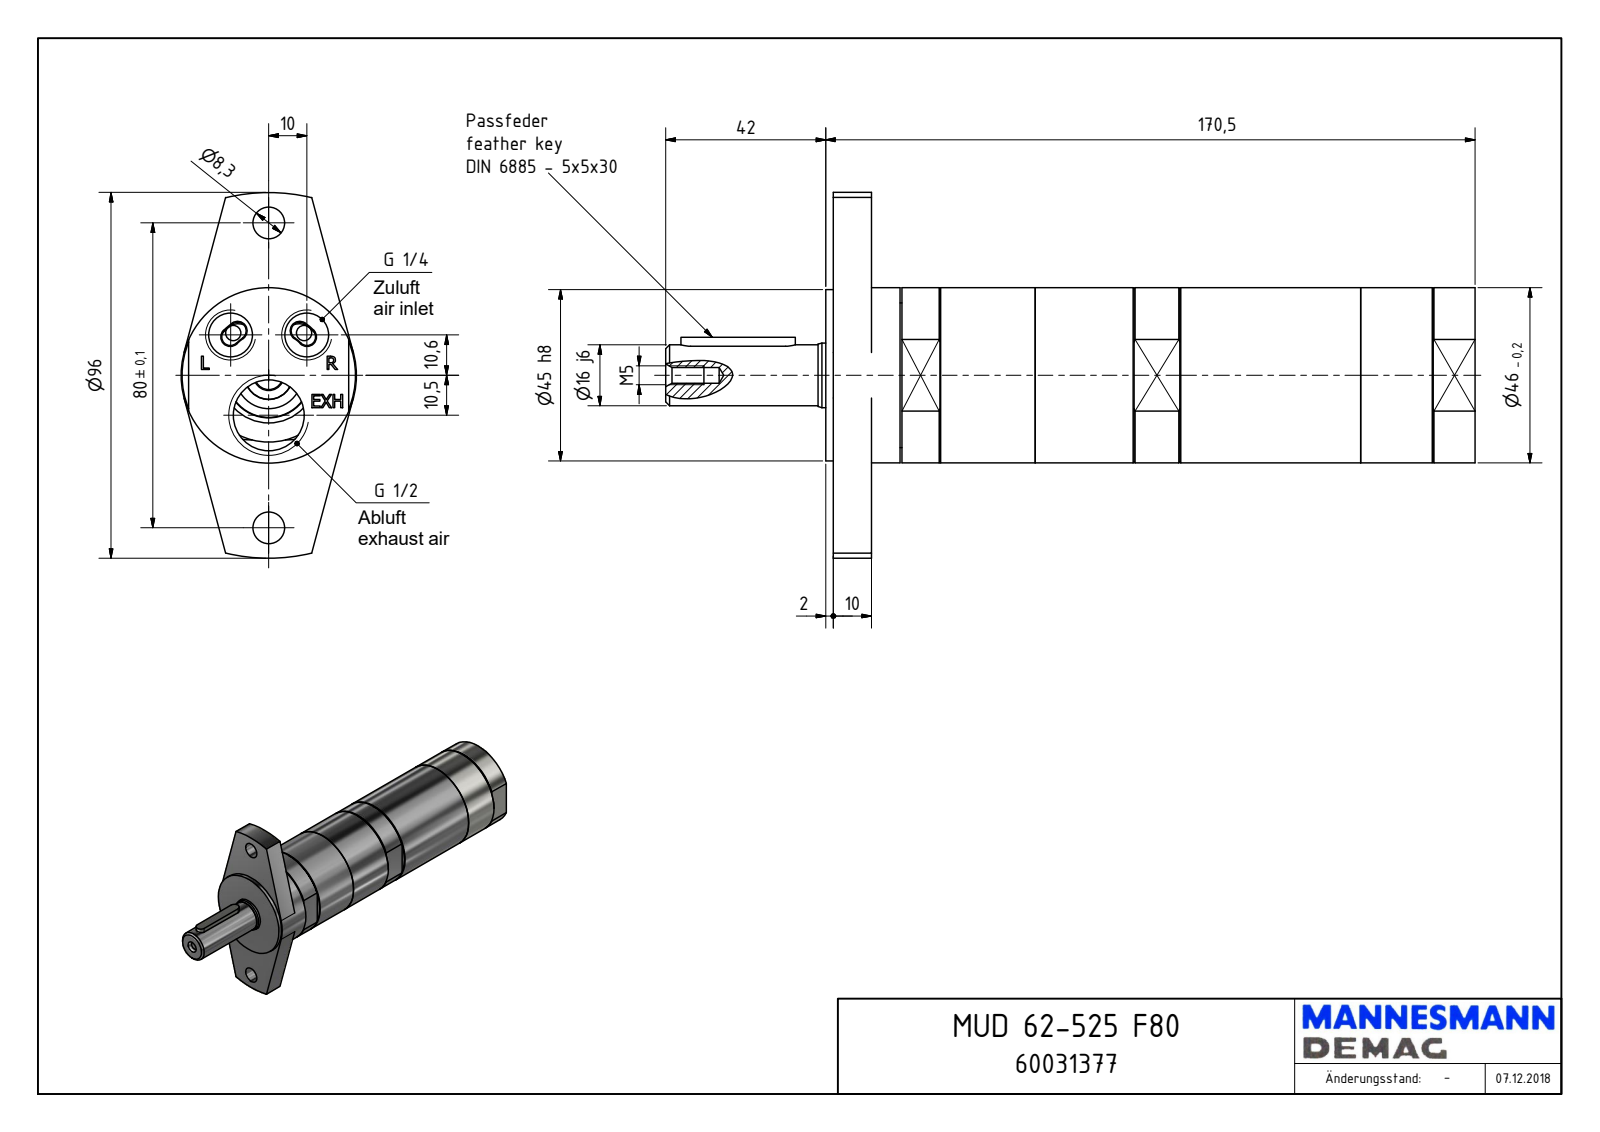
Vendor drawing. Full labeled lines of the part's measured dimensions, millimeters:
Part name (STEP PRODUCT): MUD 62-525 F80_60031377
STEP written by: Autodesk Inventor 2018 (AUTOMOTIVE_DESIGN)
Units: millimetres
Bodies: 1 solid, 185 faces (106 planar, 44 cylindrical, 35 other)
Overall size (bounding box): 212.5 × 96 × 46
Volume: 300 076 mm³ · Surface area: 39 998 mm²
Round holes (diameter × count): ⌀8.3 ×2, ⌀11.45 ×2, ⌀4.13 ×1, ⌀17.5 ×1, ⌀18.63 ×1, ⌀21.5 ×1, ⌀23 ×1, ⌀38 ×1, ⌀38.38 ×1
Round bosses / shafts (diameter × count): ⌀46 ×1, ⌀45 ×1, ⌀33.14 ×1, ⌀19.56 ×1, ⌀16.95 ×1, ⌀16 ×1
Partial cylindrical surfaces — rounded edges, fillets, slot ends (radius × count): R2.5 ×6, R5 ×2, R16.75 ×1, R48 ×1
Main face-to-face distances: 10, 12, 2, 170.5, 168.5, 158.5, 42, 8, 150.5, 18
Hole centre spacings: 14.57, 23.35, 31.05, 40, 51.58, 10.5, 20, 29.5
